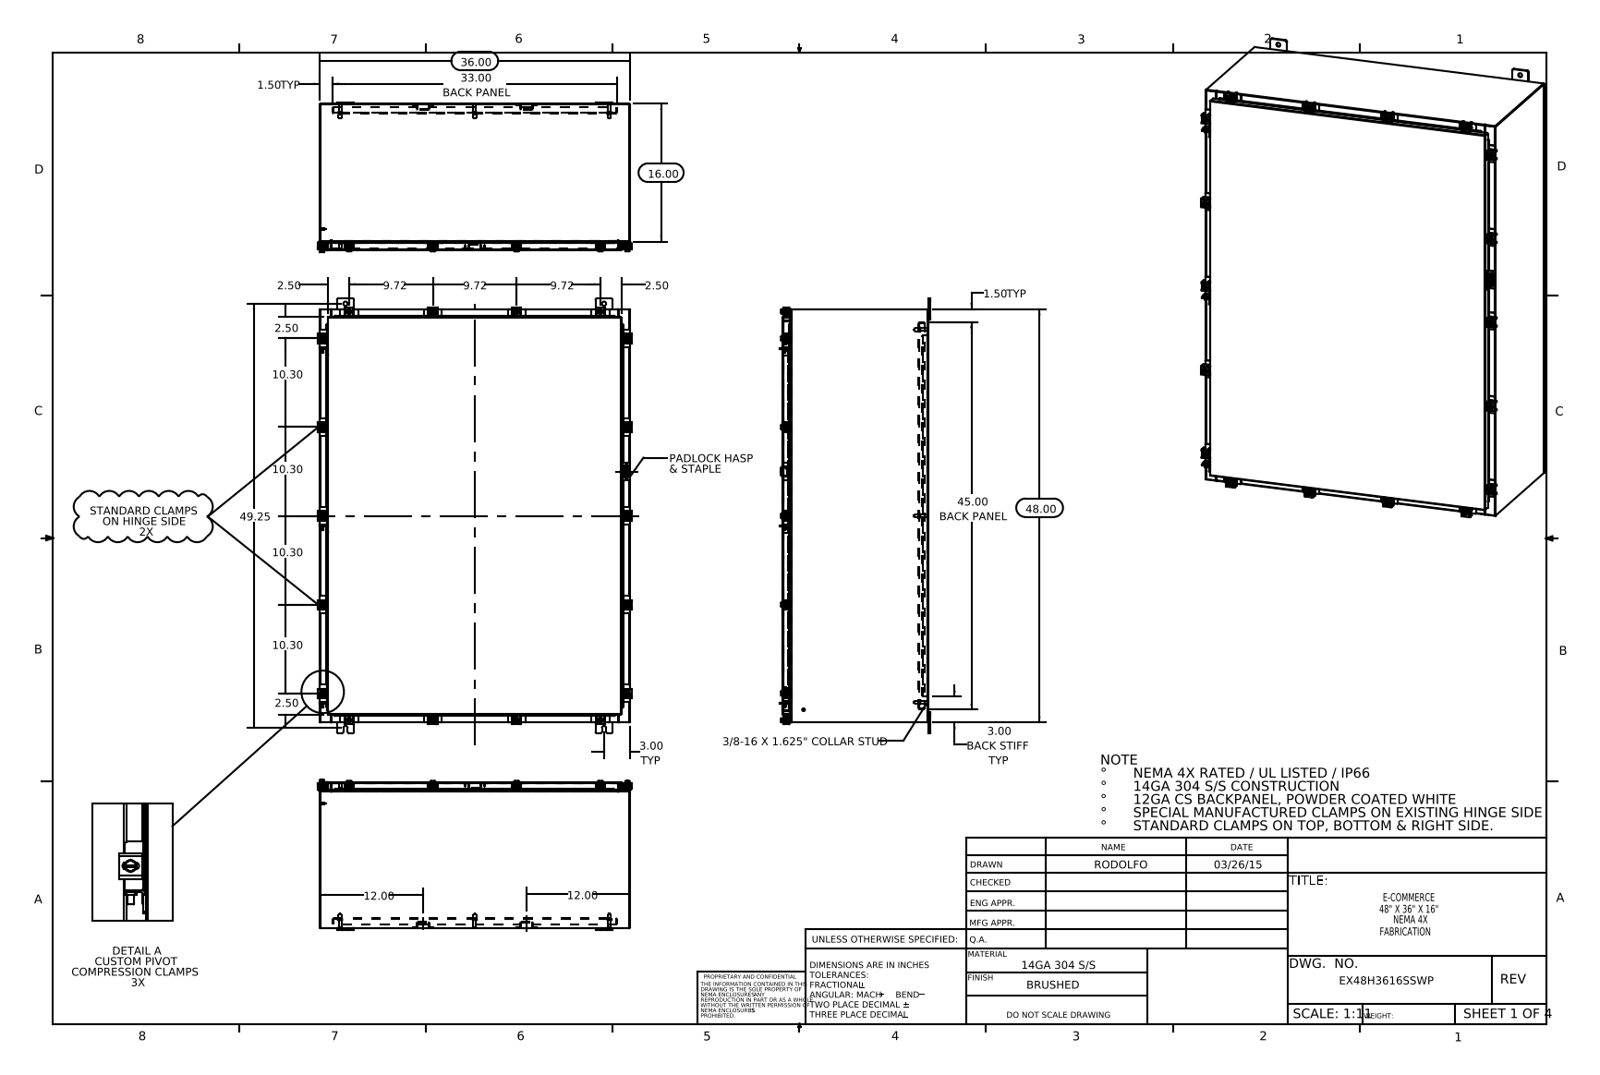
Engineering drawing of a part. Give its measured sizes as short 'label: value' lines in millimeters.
name: EX48H3616SSWP; EX48H3616SSWP Padlock Staple; EX48H3616SSWP Body; 30X10 Clamp Bracket2 (+8 more)
written by: SolidWorks 2014 (CONFIG_CONTROL_DESIGN)
unit: mm
bodies: 126 solids, 3106 faces (1613 planar, 1195 cylindrical, 298 other)
size: 1282.7 × 925.1 × 443.3
volume: 11 450 000 mm³; area: 11 280 000 mm²
holes: 18× ⌀5.4, 18× ⌀6.6, 12× ⌀12.7, 7× ⌀6.4, 1× ⌀3.2
bosses: 18× ⌀12.7, 18× ⌀6.4, 15× ⌀10.1, 8× ⌀15.9, 8× ⌀9.5, 8× ⌀8.4, 6× ⌀4, 6× ⌀3.6
rounds: 76× R1.5, 38× R0.3, 36× R3.6, 34× R2.2, 33× R3, 27× R2.3, 25× R1.3, 24× R3.7
face distances: 1.9, 429.3, 427.4, 431.2, 2.6, 912.5, 25.4, 27.3, 402, 403.9
hole spacings: 50, 59.6, 112.8, 354.9, 374.1, 409.6, 422.2, 451
